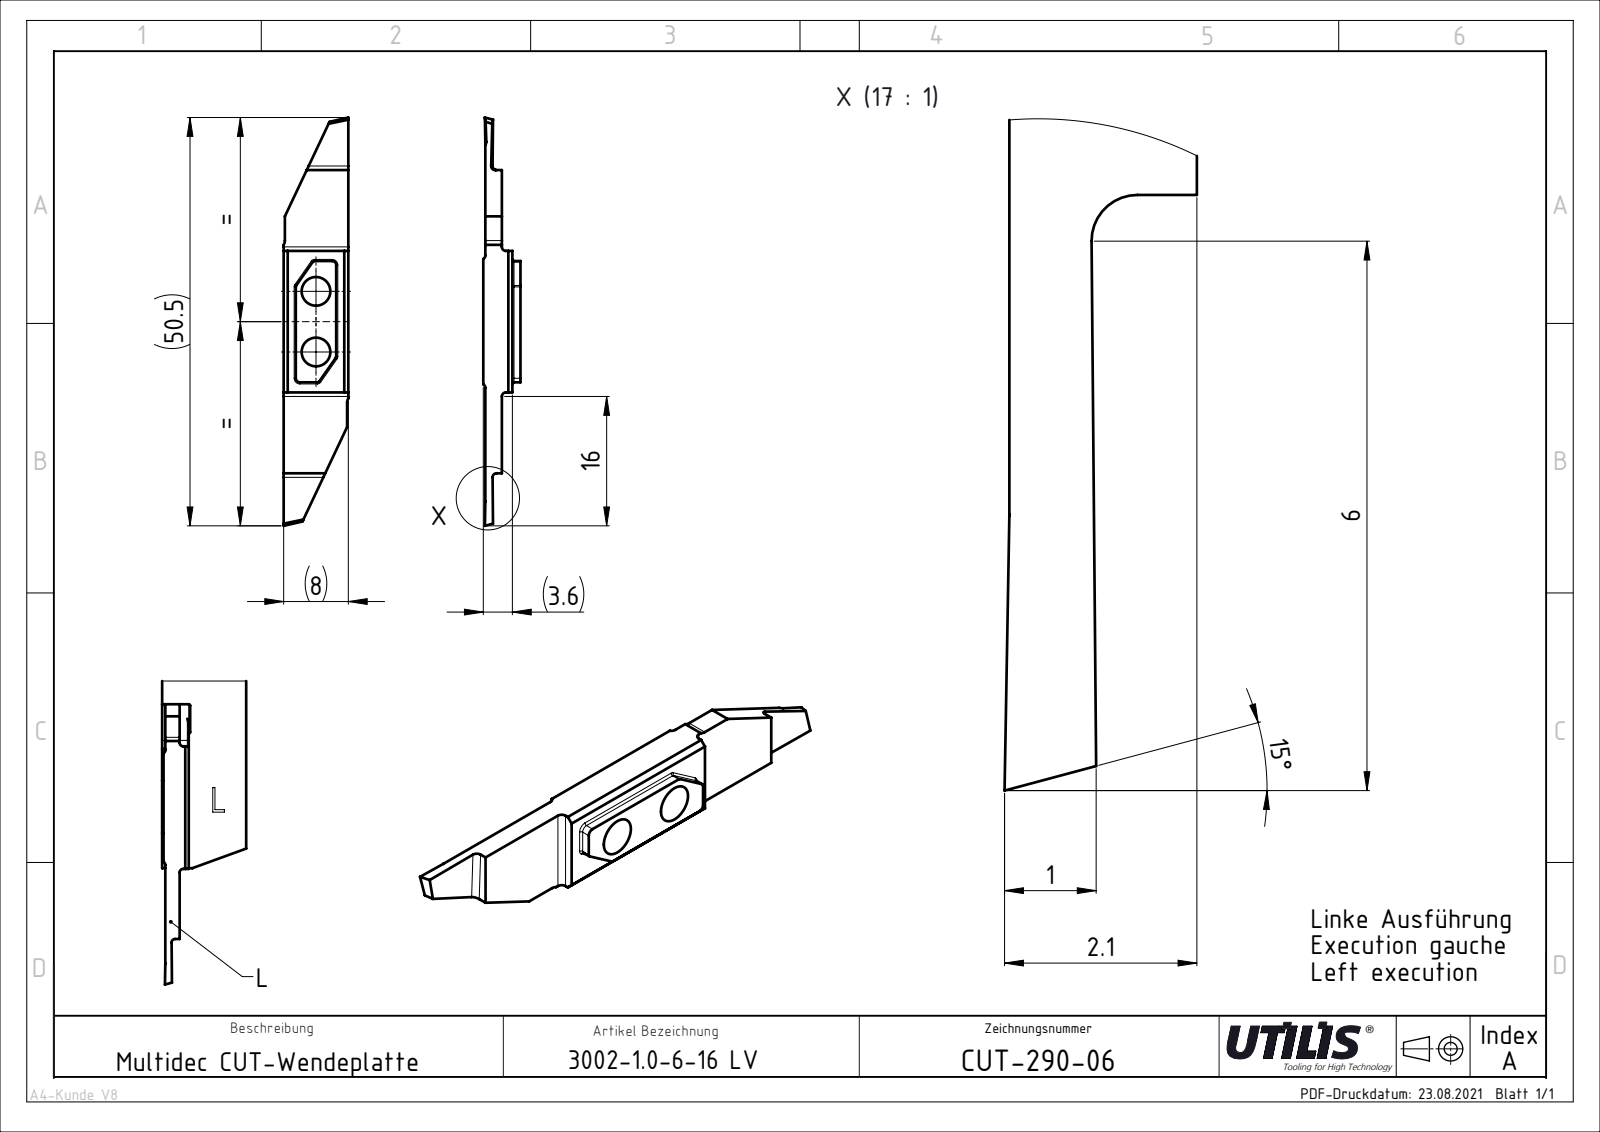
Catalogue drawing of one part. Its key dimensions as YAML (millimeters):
part_name: "CUT-290-06"
step_written_by: "SolidWorks 2016 (AUTOMOTIVE_DESIGN)"
units: millimeters
bodies: {solids: 1, faces: 38, planar: 24, cylindrical: 14, other: 0}
overall_size: [50.5, 8, 3.55]
volume: 757
surface_area: 956
round_holes:
  - {diameter: 3.55, count: 2}
partial_cylinders:
  - {radius: 0.5, count: 6}
  - {radius: 0.15, count: 2}
  - {radius: 1, count: 2}
face_to_face_distances: [2.05, 3.3, 1.25, 2.3, 3.55, 8, 18.1, 7.85, 7.7, 10]
hole_center_spacings: [7.5]
